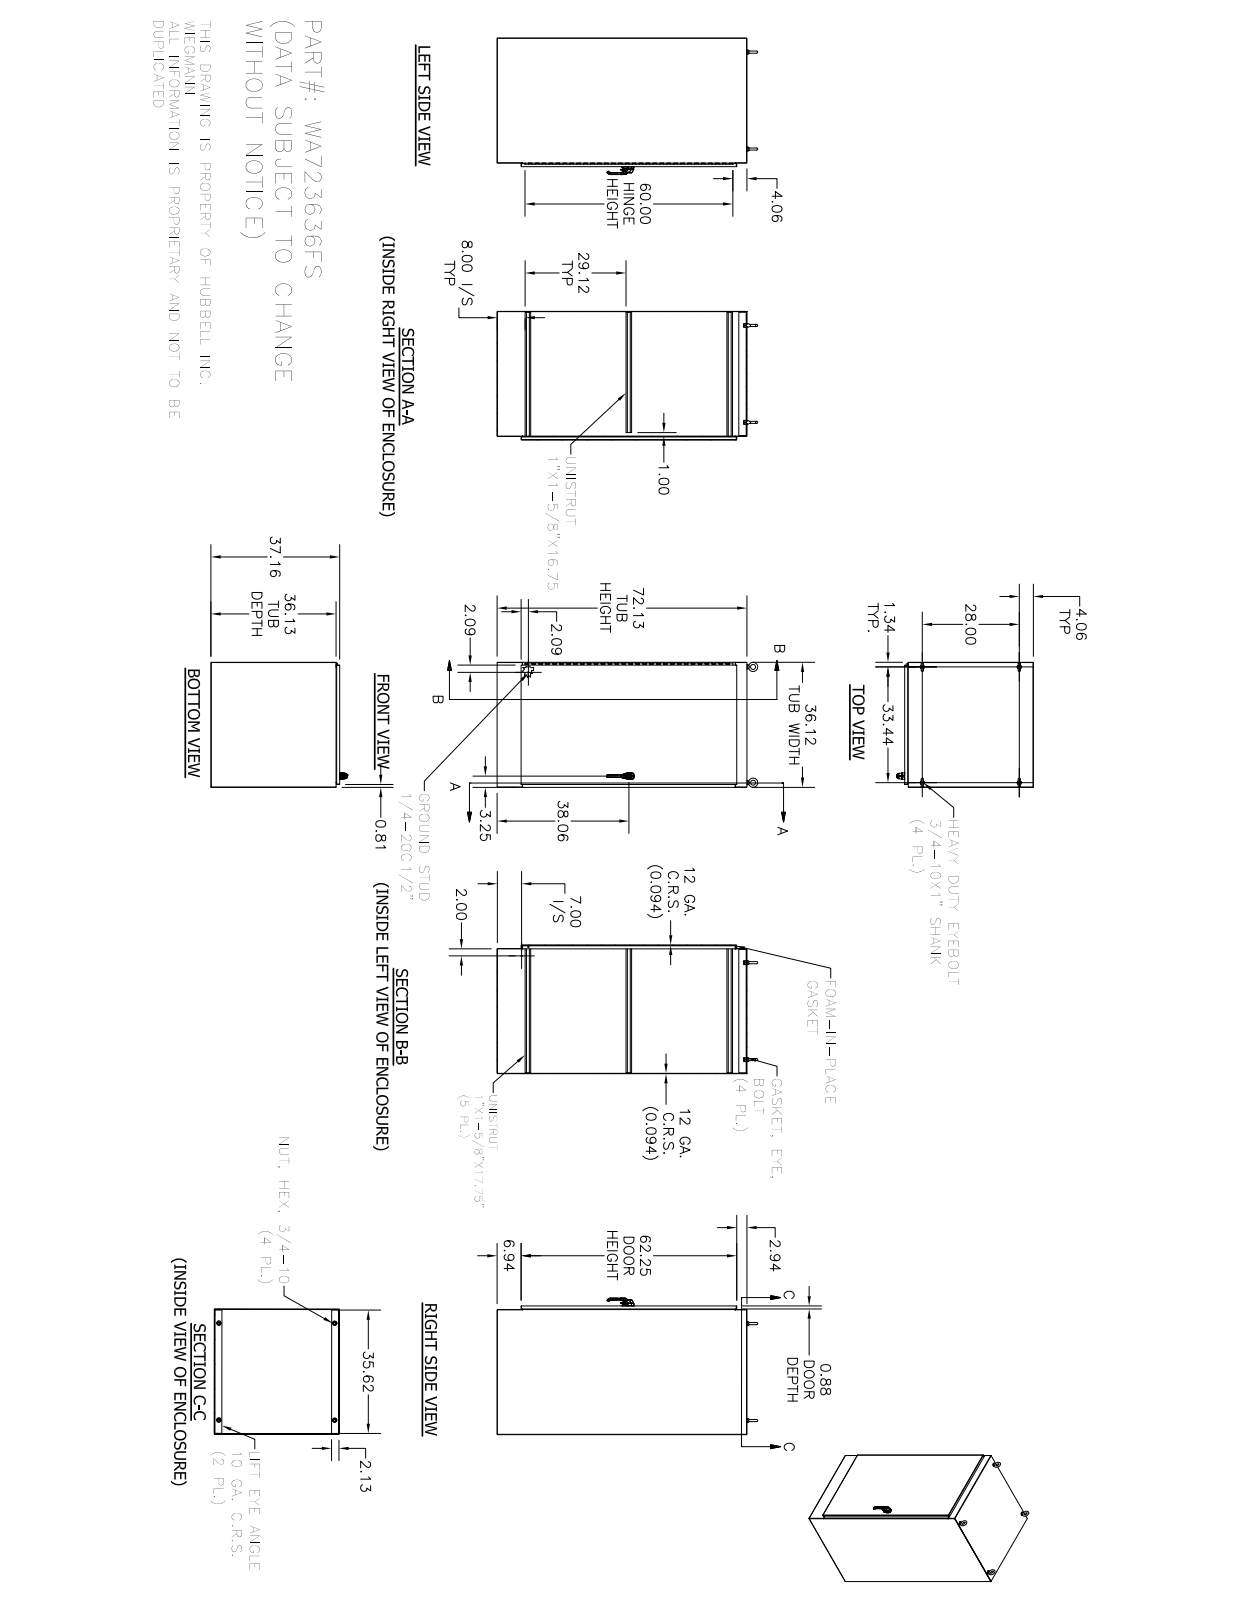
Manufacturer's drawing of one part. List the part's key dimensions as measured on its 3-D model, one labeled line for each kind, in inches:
Part name (STEP PRODUCT): WA7236FSFB; WA7236FSLS; WA7236FSRS; WA3636FSBTM (+8 more)
STEP written by: Autodesk Inventor 2014 (AUTOMOTIVE_DESIGN)
Units: inches
Bodies: 53 solids, 3001 faces (1236 planar, 1025 cylindrical, 740 other)
Overall size (bounding box): 75.248 × 39.409 × 36.125
Volume: 1 408 in³ · Surface area: 29 680 in²
Round holes (diameter × count): ⌀0.276 ×8, ⌀0.2 ×4, ⌀0.642 ×4, ⌀0.813 ×4, ⌀0.213 ×3, ⌀0.28 ×3, ⌀0.315 ×2, ⌀0.402 ×2, ⌀0.407 ×2, ⌀0.413 ×2, ⌀0.122 ×1, ⌀0.124 ×1
Round bosses / shafts (diameter × count): ⌀1.25 ×4, ⌀1.12 ×4, ⌀0.75 ×4, ⌀0.25 ×3, ⌀0.531 ×2, ⌀0.526 ×2, ⌀0.435 ×2, ⌀0.337 ×2
Partial cylindrical surfaces — rounded edges, fillets, slot ends (radius × count): R0.02 ×178, R0.012 ×101, R0.019 ×23, R0.01 ×16, R0.031 ×14, R0.079 ×14, R0.019 ×12, R0.053 ×12
Main face-to-face distances: 0.094, 36.031, 37.067, 35.938, 36.125, 72.031, 36.973, 37.16, 71.938, 72.125
Hole centre spacings: 0.381, 0.381, 0.383, 0.762, 0.764, 0.886, 1.144, 1.271
